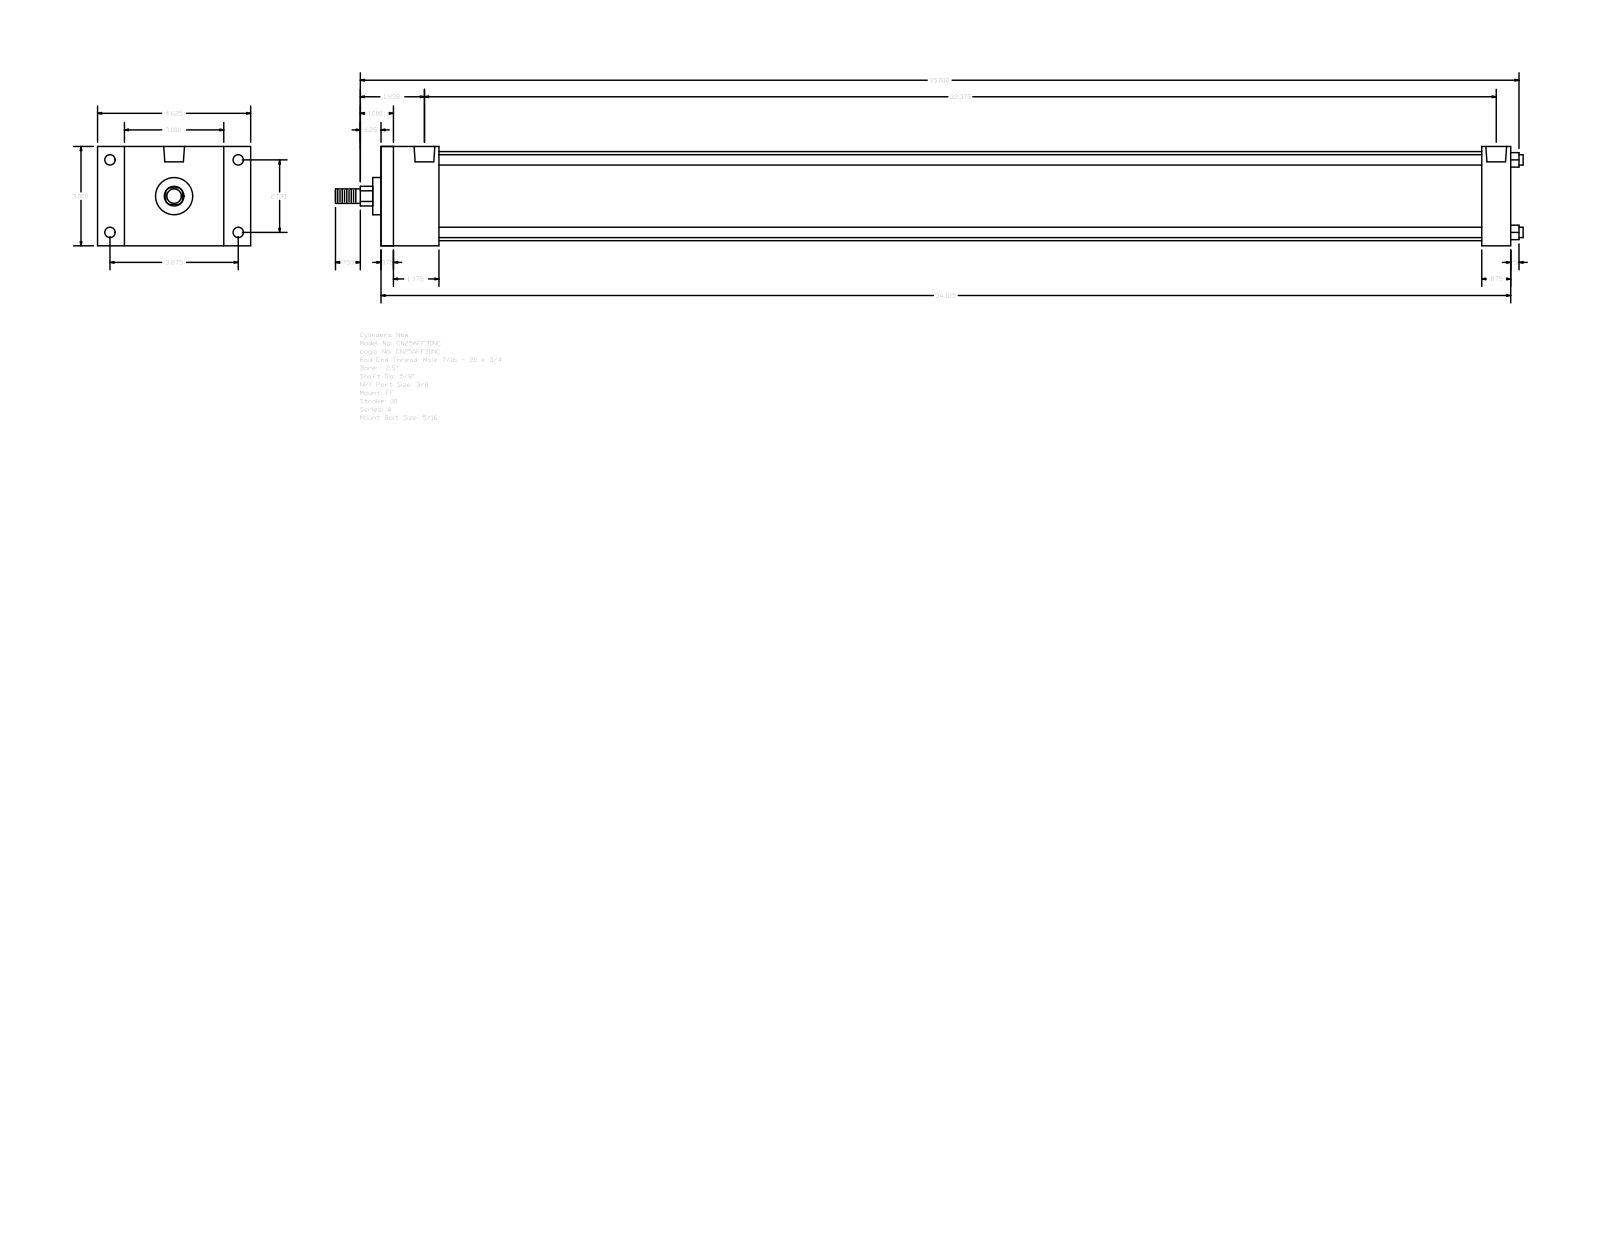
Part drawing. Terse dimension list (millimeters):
name: A_FF__0250_0.625
written by: GSSL Pune (CONFIG_CONTROL_DESIGN)
unit: mm
bodies: 0 solids, 92 faces (64 planar, 28 cylindrical, 0 other)
size: 911.23 × 117.47 × 76.2
holes: 4× ⌀5.56, 4× ⌀7.94, 2× ⌀15.93
bosses: 4× ⌀7.94, 1× ⌀68.33, 1× ⌀28.57, 1× ⌀15.88, 1× ⌀11.11
rounds: 1× R7.54
face distances: 76.2, 866.77, 9.52, 857.25, 44.45, 34.93, 844.54, 835.02, 800.09, 822.32
hole spacings: 2.38, 55.62, 98.42, 113.05, 824.71, 827.09, 822.33
